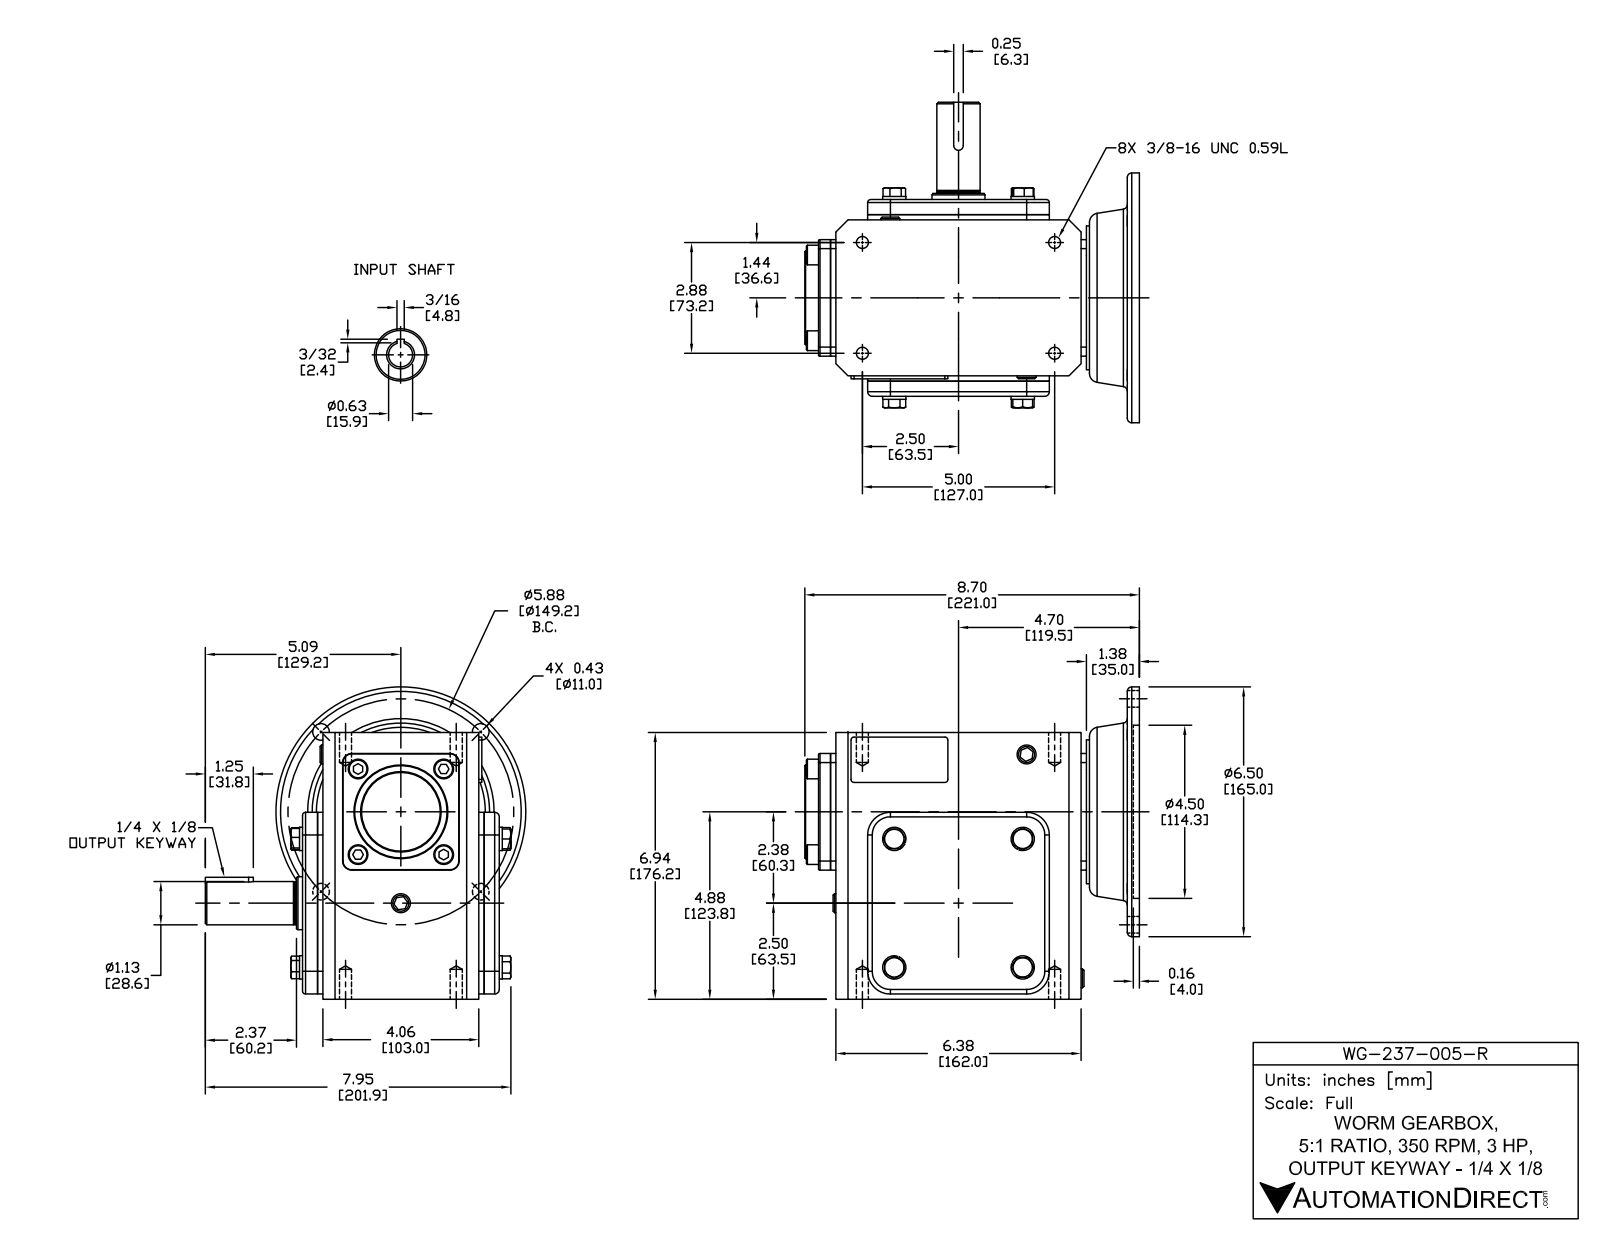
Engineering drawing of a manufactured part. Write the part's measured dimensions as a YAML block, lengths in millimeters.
part_name: "WG-237-005-R"
step_written_by: "SolidWorks 2015 (CONFIG_CONTROL_DESIGN)"
units: millimeters
bodies: {solids: 37, faces: 537, planar: 294, cylindrical: 153, other: 90}
overall_size: [221, 211.7, 206.3]
volume: 3644000
surface_area: 327900
round_holes:
  - {diameter: 8, count: 4}
  - {diameter: 10.3, count: 4}
  - {diameter: 15, count: 1}
  - {diameter: 15.9, count: 1}
  - {diameter: 35, count: 1}
  - {diameter: 37, count: 1}
  - {diameter: 45, count: 1}
  - {diameter: 97, count: 1}
  - {diameter: 114.3, count: 1}
round_bosses_or_shafts:
  - {diameter: 15.4, count: 4}
  - {diameter: 13, count: 4}
  - {diameter: 165, count: 1}
  - {diameter: 95, count: 1}
  - {diameter: 62, count: 1}
  - {diameter: 52, count: 1}
  - {diameter: 30, count: 1}
  - {diameter: 29, count: 1}
partial_cylinders:
  - {radius: 2, count: 12}
  - {radius: 6, count: 6}
  - {radius: 3, count: 4}
  - {radius: 15, count: 4}
  - {radius: 0.5, count: 2}
  - {radius: 1, count: 2}
  - {radius: 3.2, count: 1}
face_to_face_distances: [3.5, 120, 10, 110, 13.5, 116.5, 106.5, 165.5, 176.2, 8]
hole_center_spacings: [74.6, 53.3, 73.2, 105.5, 105.5, 124.8, 127, 146.6]
